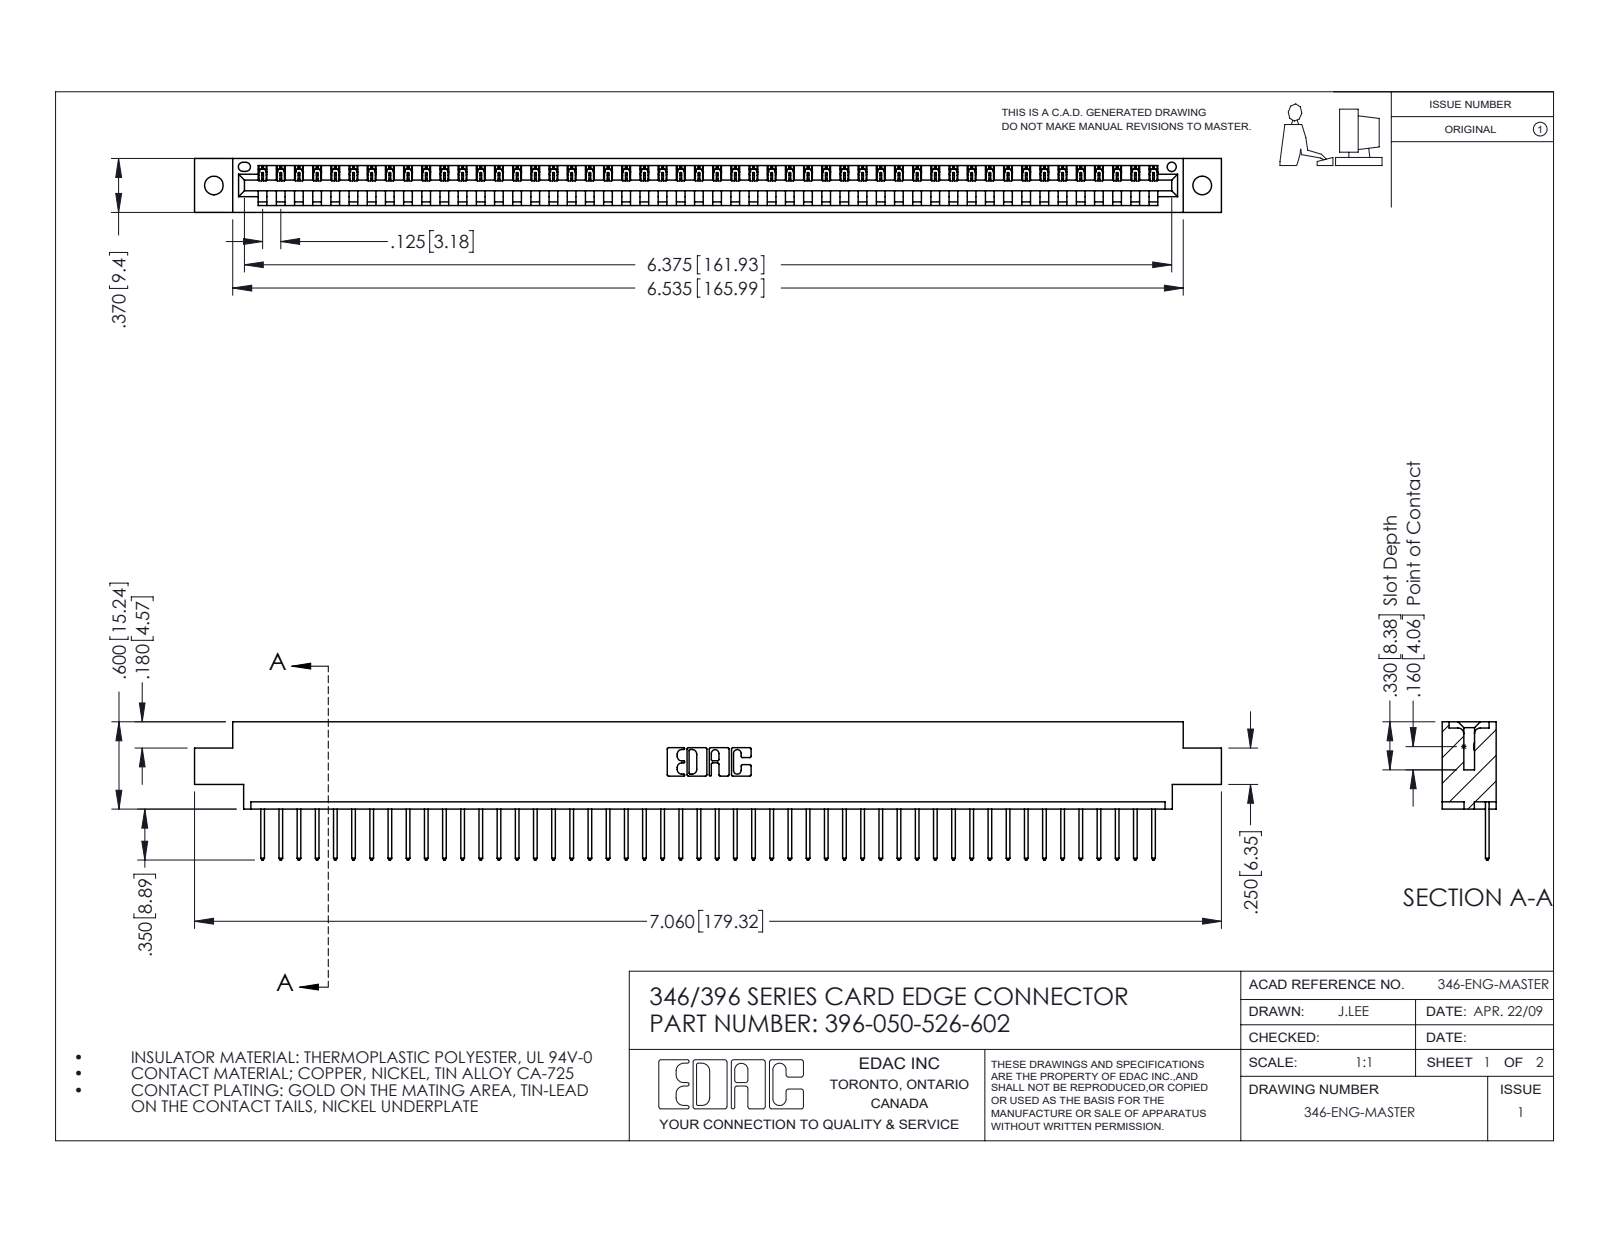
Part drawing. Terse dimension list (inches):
name: 346 Part_0.170 Offset - 0.128 Dia; 345-292-001_345-293-126; 396-050-526-602
written by: SolidWorks 2016 (CONFIG_CONTROL_DESIGN)
unit: in
bodies: 51 solids, 3026 faces (2080 planar, 946 cylindrical, 0 other)
size: 7.06 × 0.95 × 0.37
volume: 1.037 in³; area: 32.8 in²
holes: 2× ⌀0.128, 1× ⌀0.064
rounds: 100× R0.006, 100× R0.01, 22× R0.01, 6× R0.007, 6× R0.031, 3× R0.026, 2× R0.031, 2× R0.04
face distances: 0.048, 0.322, 0.37, 0.25, 0.072, 0.298, 0.025, 0.148, 0.222, 0.1
hole spacings: 0.246, 6.586, 6.795
